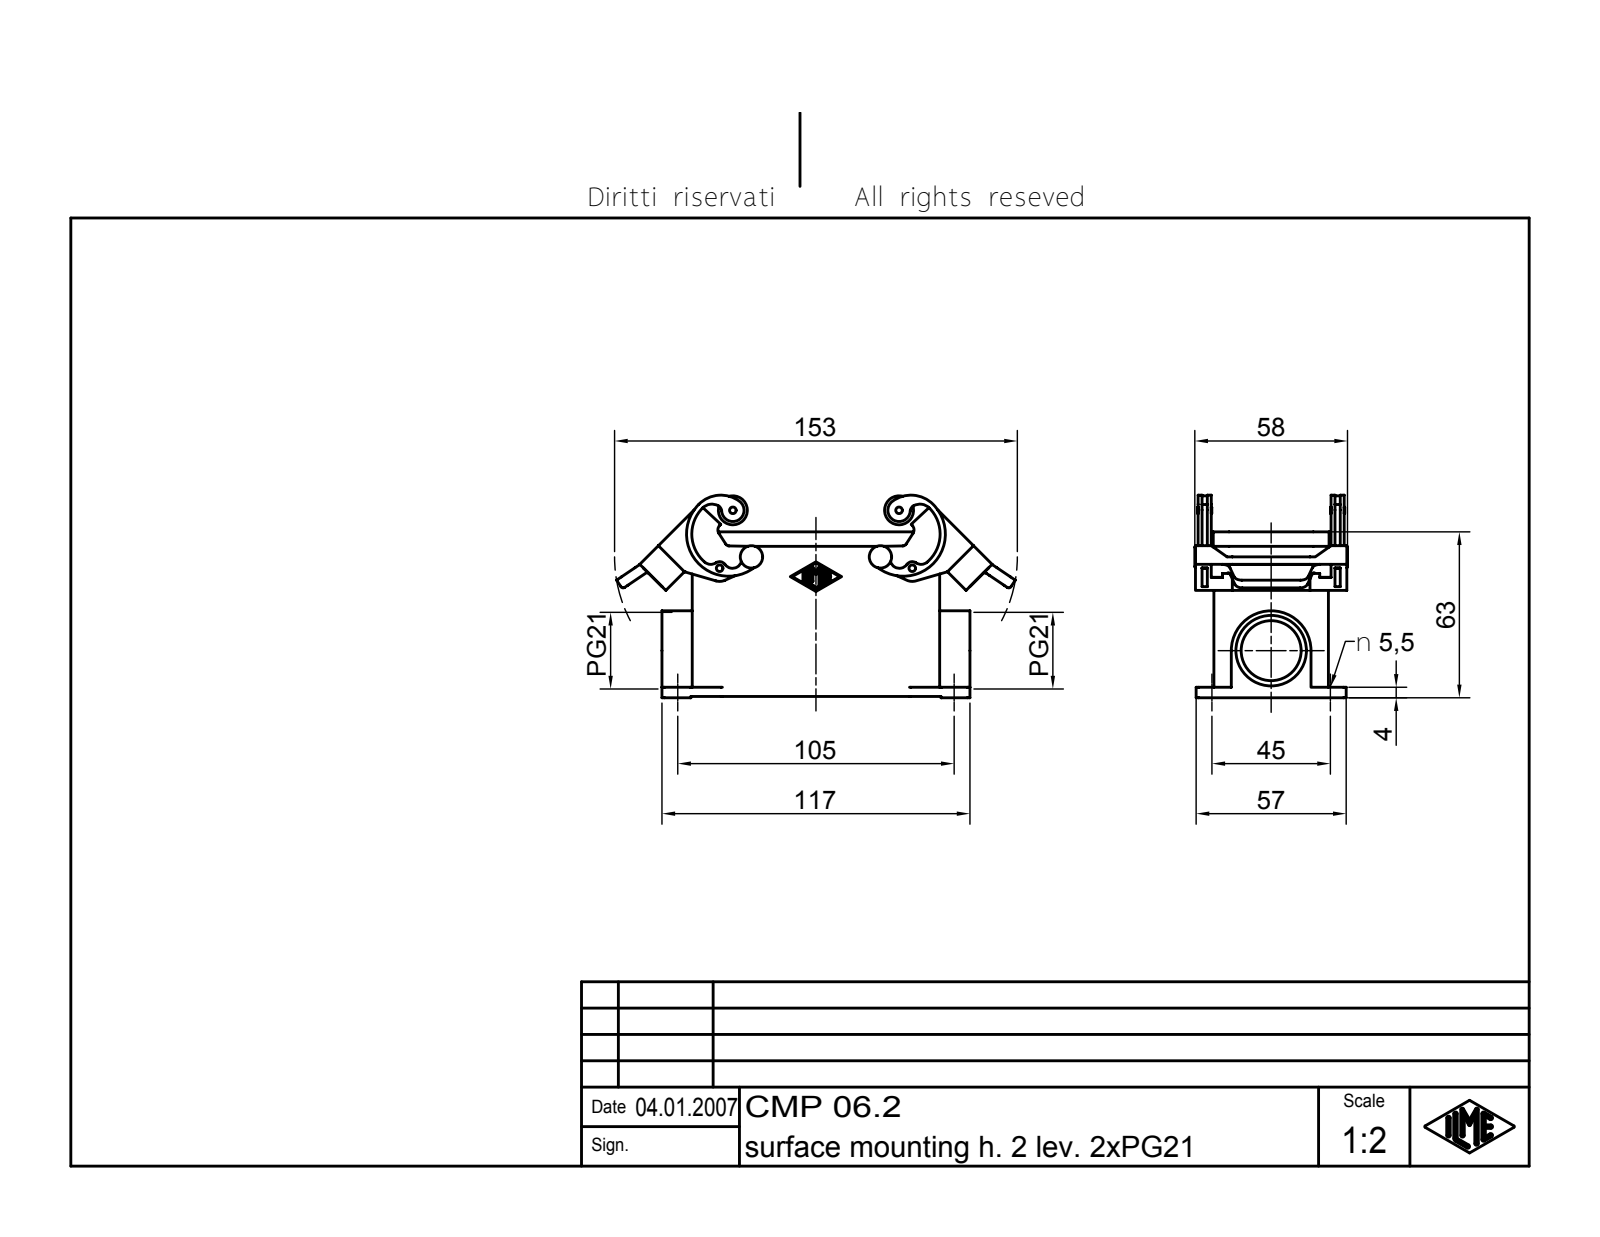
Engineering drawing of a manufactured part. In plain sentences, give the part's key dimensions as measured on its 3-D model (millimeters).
The part is named "CMP 06.2". Its 3-D file was written by "Autodesk Inventor 7 (AUTOMOTIVE_DESIGN)". It is 1 solid with 748 faces: 191 planar, 205 cylindrical and 352 other. Overall it measures 151.49 by 76.94 by 58 millimeters. Its volume is 104 960 cubic millimeters and its surface area 61 679 square millimeters. Round holes: 4 of diameter 2, 4 of diameter 5.5, 2 of diameter 2.5, 1 of diameter 22.78, 1 of diameter 26.78. Round bosses or shafts: 2 of diameter 11, 2 of diameter 5, 2 of diameter 3. Partial cylindrical surfaces (rounded edges, fillets, slot ends): 20 of radius 1, 14 of radius 0.38, 12 of radius 3, 8 of radius 6, 6 of radius 2.5, 4 of radius 1.5, 4 of radius 2, 4 of radius 3.5. The main face-to-face distances are 3, 40.5, 43.5, 3.5, 37.5, 4, 50.5, 0.75, 40.75, 4.5. The hole center spacings are 22.56, 45, 71.62, 105, 114.24, 63.14, 73.18.
